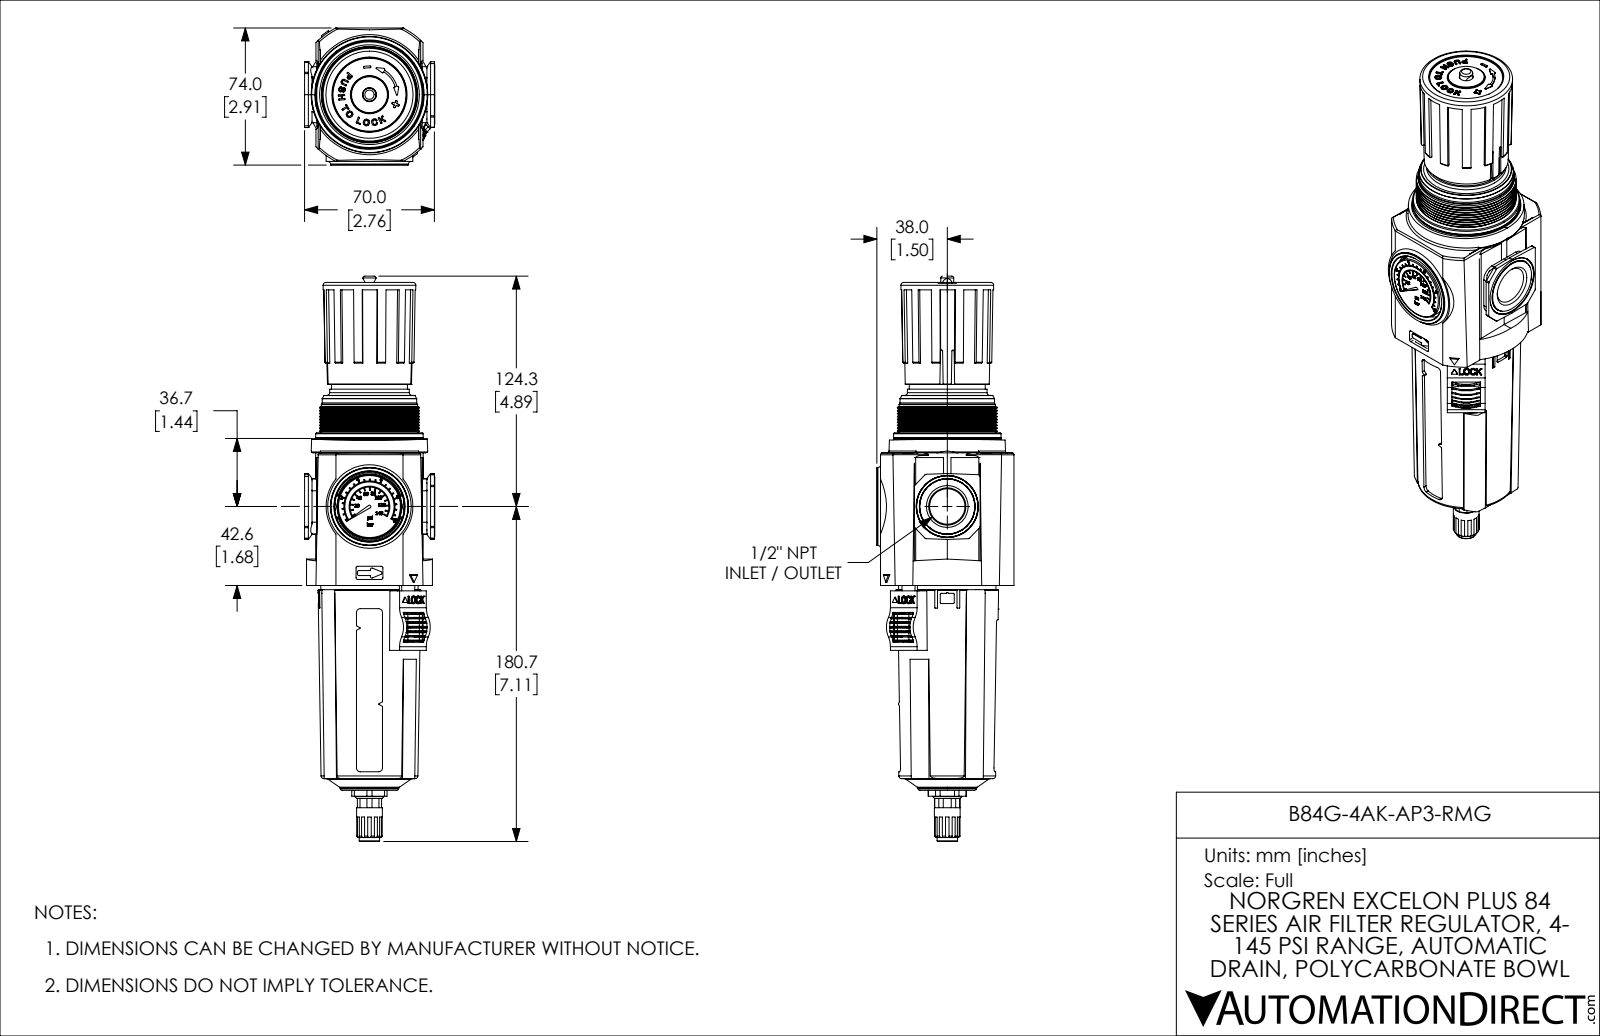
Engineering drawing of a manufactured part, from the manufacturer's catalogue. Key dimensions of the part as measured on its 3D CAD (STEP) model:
Part name (STEP PRODUCT): B84G-4AK-AP3-RMG
STEP written by: SolidWorks 2021 (CONFIG_CONTROL_DESIGN)
Units: inches
Bodies: 8 solids, 2561 faces (955 planar, 1193 cylindrical, 413 other)
Overall size (bounding box): 12.005 × 2.913 × 2.766
Volume: 45.92 in³ · Surface area: 207.6 in²
Round holes (diameter × count): ⌀0.177 ×2, ⌀0.059 ×1, ⌀0.197 ×1, ⌀0.22 ×1, ⌀0.246 ×1, ⌀0.776 ×1, ⌀0.969 ×1, ⌀1.319 ×1, ⌀2.323 ×1, ⌀2.461 ×1
Round bosses / shafts (diameter × count): ⌀0.299 ×2, ⌀0.157 ×2, ⌀2.283 ×1, ⌀2.119 ×1, ⌀2.047 ×1, ⌀2.026 ×1, ⌀2.008 ×1, ⌀1.693 ×1
Partial cylindrical surfaces — rounded edges, fillets, slot ends (radius × count): R0.039 ×34, R0.012 ×27, R0.02 ×26, R0.01 ×24, R0.047 ×18, R0.028 ×16, R0.03 ×16, R0.004 ×14
Main face-to-face distances: 2.719, 2.323, 0.035, 2.683, 0.512, 0.622, 2.096, 2.061, 3.866, 3.831
Hole centre spacings: 0.856, 1.713
